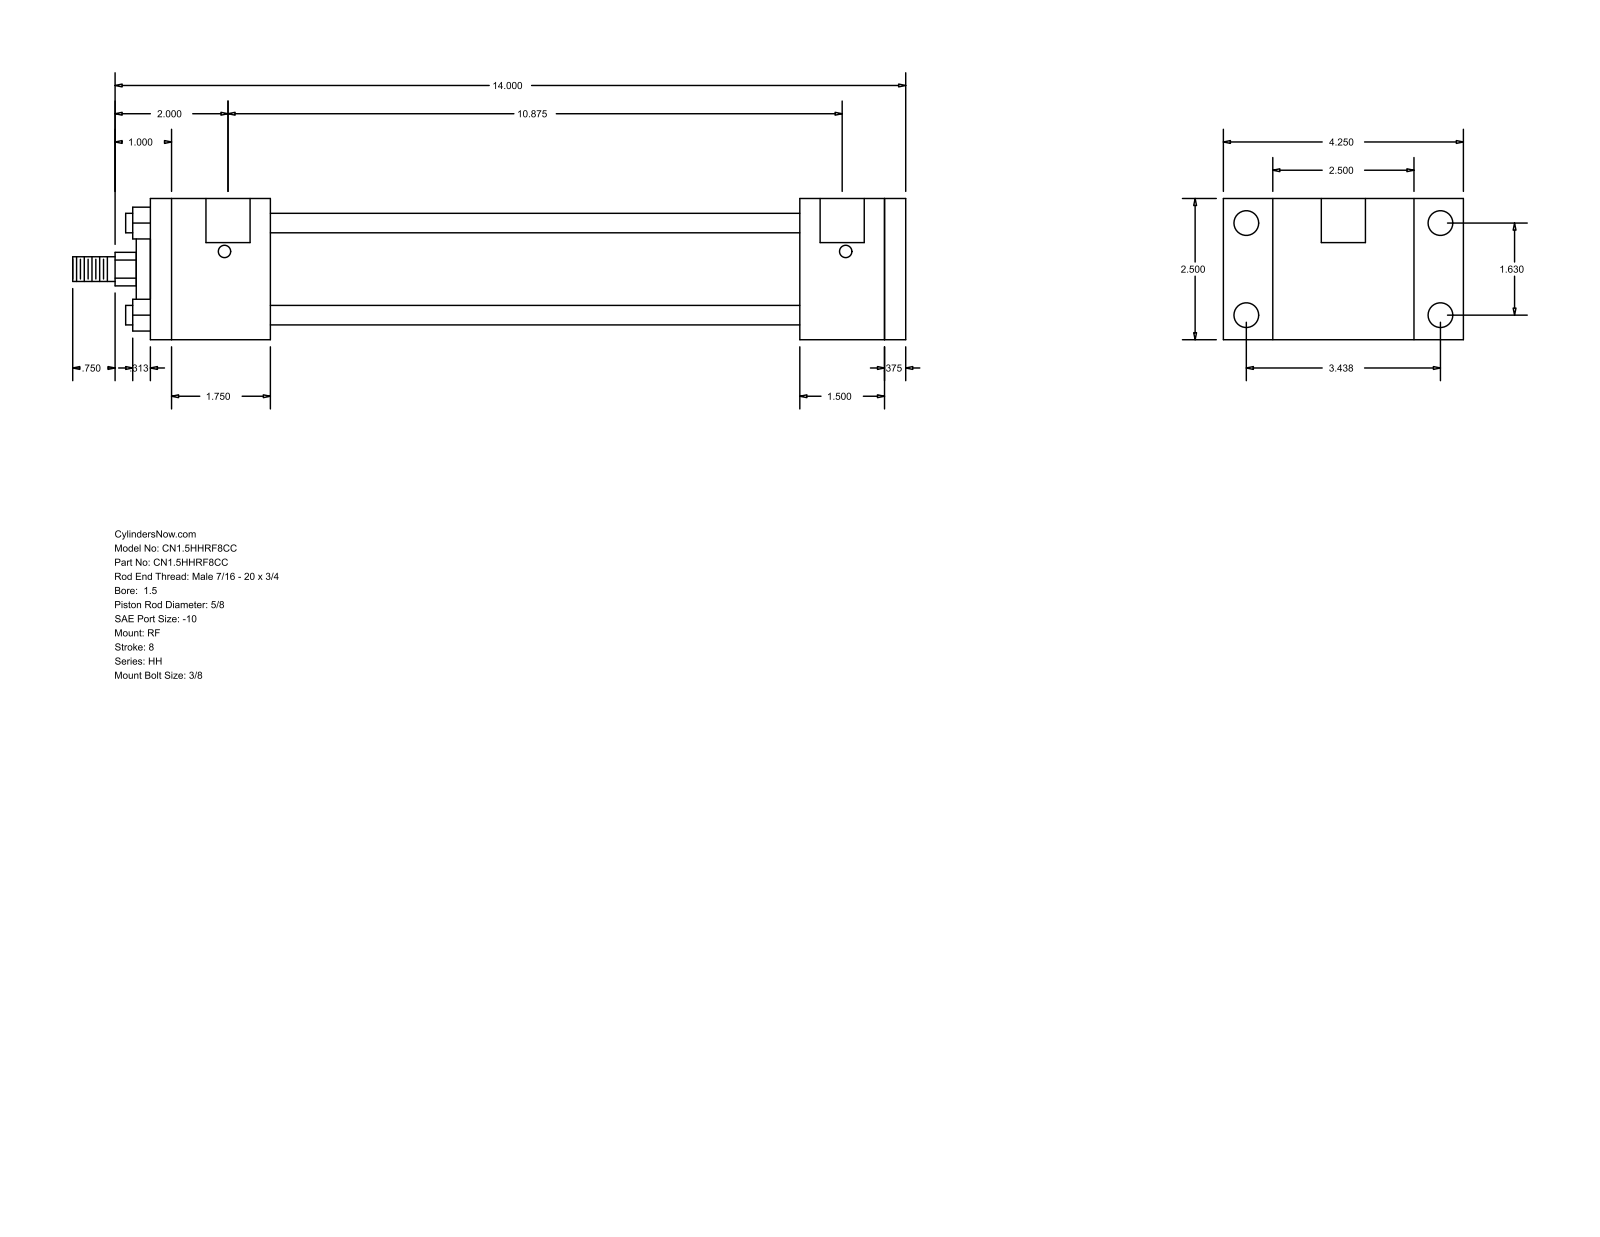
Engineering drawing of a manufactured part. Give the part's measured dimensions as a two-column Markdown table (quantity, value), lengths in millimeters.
| quantity | value |
| --- | --- |
| part name | HH_RF__0150_0.625 |
| STEP written by | GSSL Pune (CONFIG_CONTROL_DESIGN) |
| units | millimeters |
| bodies | 0 solids, 92 faces (64 planar, 28 cylindrical, 0 other) |
| overall size | 374.65 × 107.95 × 63.5 |
| round holes (diameter × count) | 5.56 × 4, 11.13 × 4, 19.84 × 2 |
| round bosses / shafts (diameter × count) | 8.76 × 4, 44.45 × 1, 28.57 × 1, 15.88 × 1, 11.11 × 1 |
| partial cylindrical surfaces (radius × count) | 7.54 × 1 |
| main face-to-face distances | 63.5, 339.72, 9.53, 330.19, 53.97, 292.1, 238.13, 276.22, 285.75, 38.09 |
| hole center spacings | 1.59, 41.4, 87.32, 96.64, 277.81, 279.4, 276.22 |
